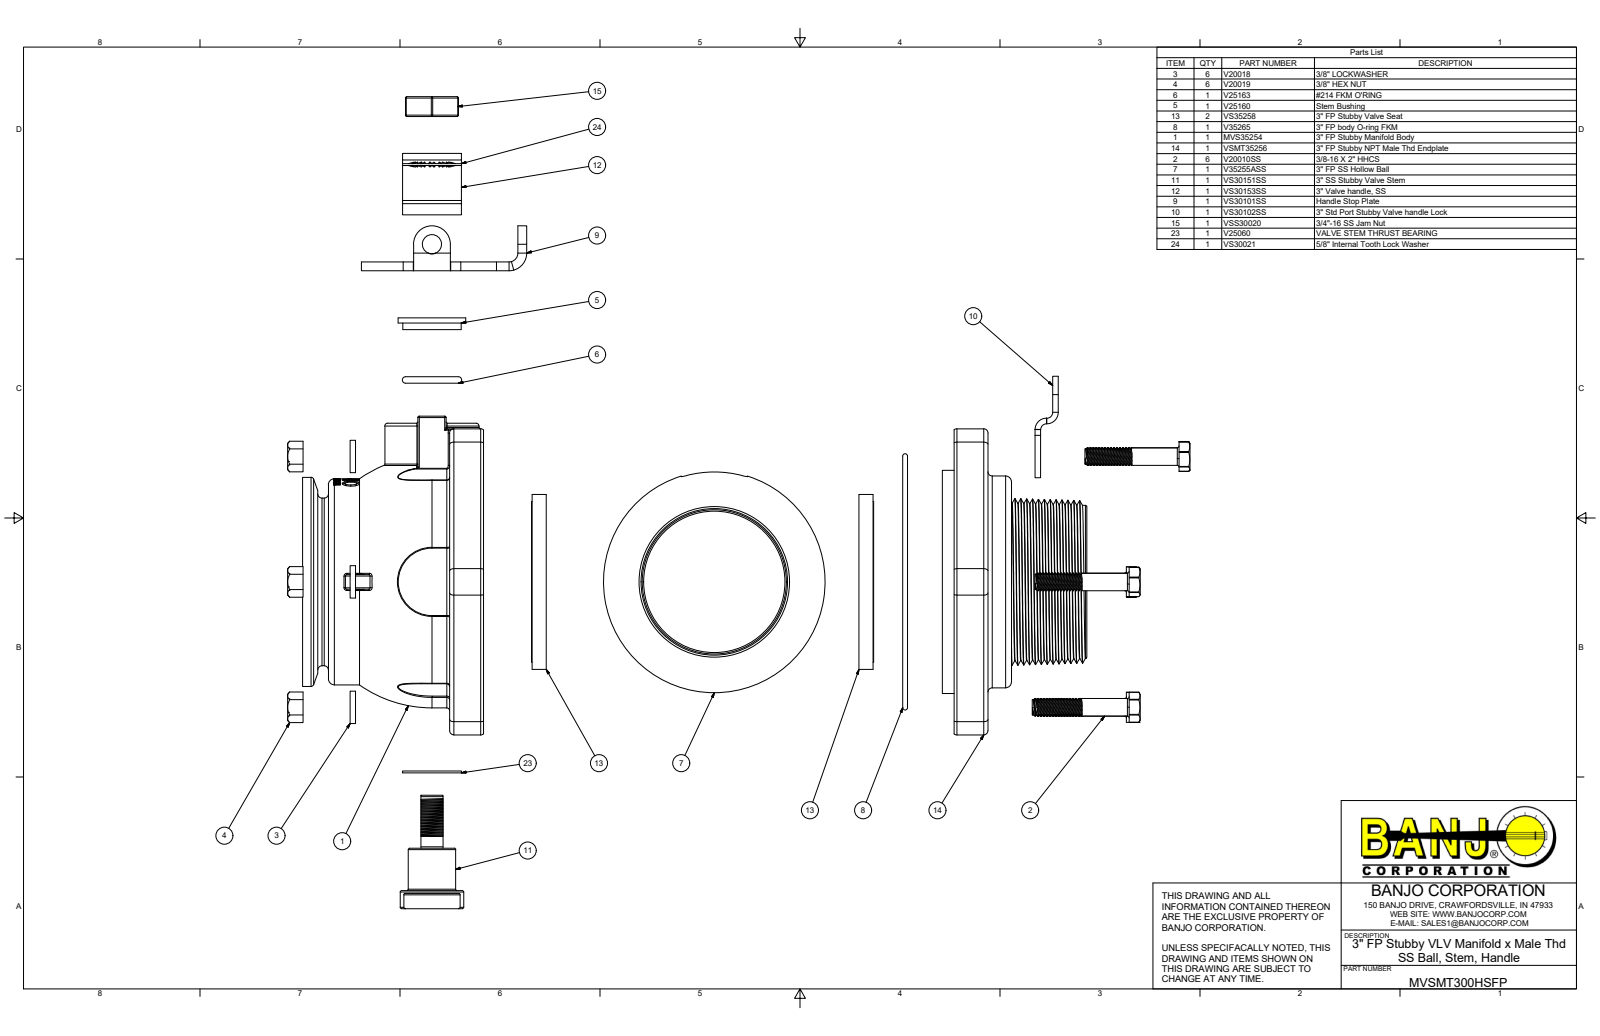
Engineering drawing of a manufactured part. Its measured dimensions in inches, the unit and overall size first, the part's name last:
Units: inches
Overall size (bounding box): 13.526 × 8.16 × 6.665
Round holes (diameter × count): ⌀0.307 ×6, ⌀0.385 ×6, ⌀0.44 ×6, ⌀0.406 ×3, ⌀3 ×3, ⌀0.25 ×2, ⌀0.375 ×2, ⌀0.7 ×1, ⌀1 ×1, ⌀1.005 ×1, ⌀1.016 ×1, ⌀1.245 ×1
Round bosses / shafts (diameter × count): ⌀0.324 ×90, ⌀0.687 ×6, ⌀0.375 ×6, ⌀5.16 ×1, ⌀4.74 ×1, ⌀4.5 ×1, ⌀4.44 ×1, ⌀4.375 ×1
Partial cylindrical surfaces — rounded edges, fillets, slot ends (radius × count): R0.03 ×61, R0.09 ×24, R0.162 ×12, R0.06 ×10, R0.32 ×6, R0.5 ×6, R0.563 ×6, R0.375 ×5
Main face-to-face distances: 0.72, 0.236, 1.44, 6.5, 1.067, 1.303, 0.188, 1.256, 1.491, 1.25
Hole centre spacings: 3.075, 3.075, 5.326, 3.982, 5.028, 6.15, 2.023, 2.026
Volume: 70.42 in³ · Surface area: 572 in²
Bodies: 33 solids, 2332 faces (390 planar, 901 cylindrical, 1041 other)
Part name (STEP PRODUCT): MVSMT300HSFP; MVS35254; MVS35254X; VSMT35256 (+8 more)
STEP written by: Autodesk Inventor 2017 (AUTOMOTIVE_DESIGN)
